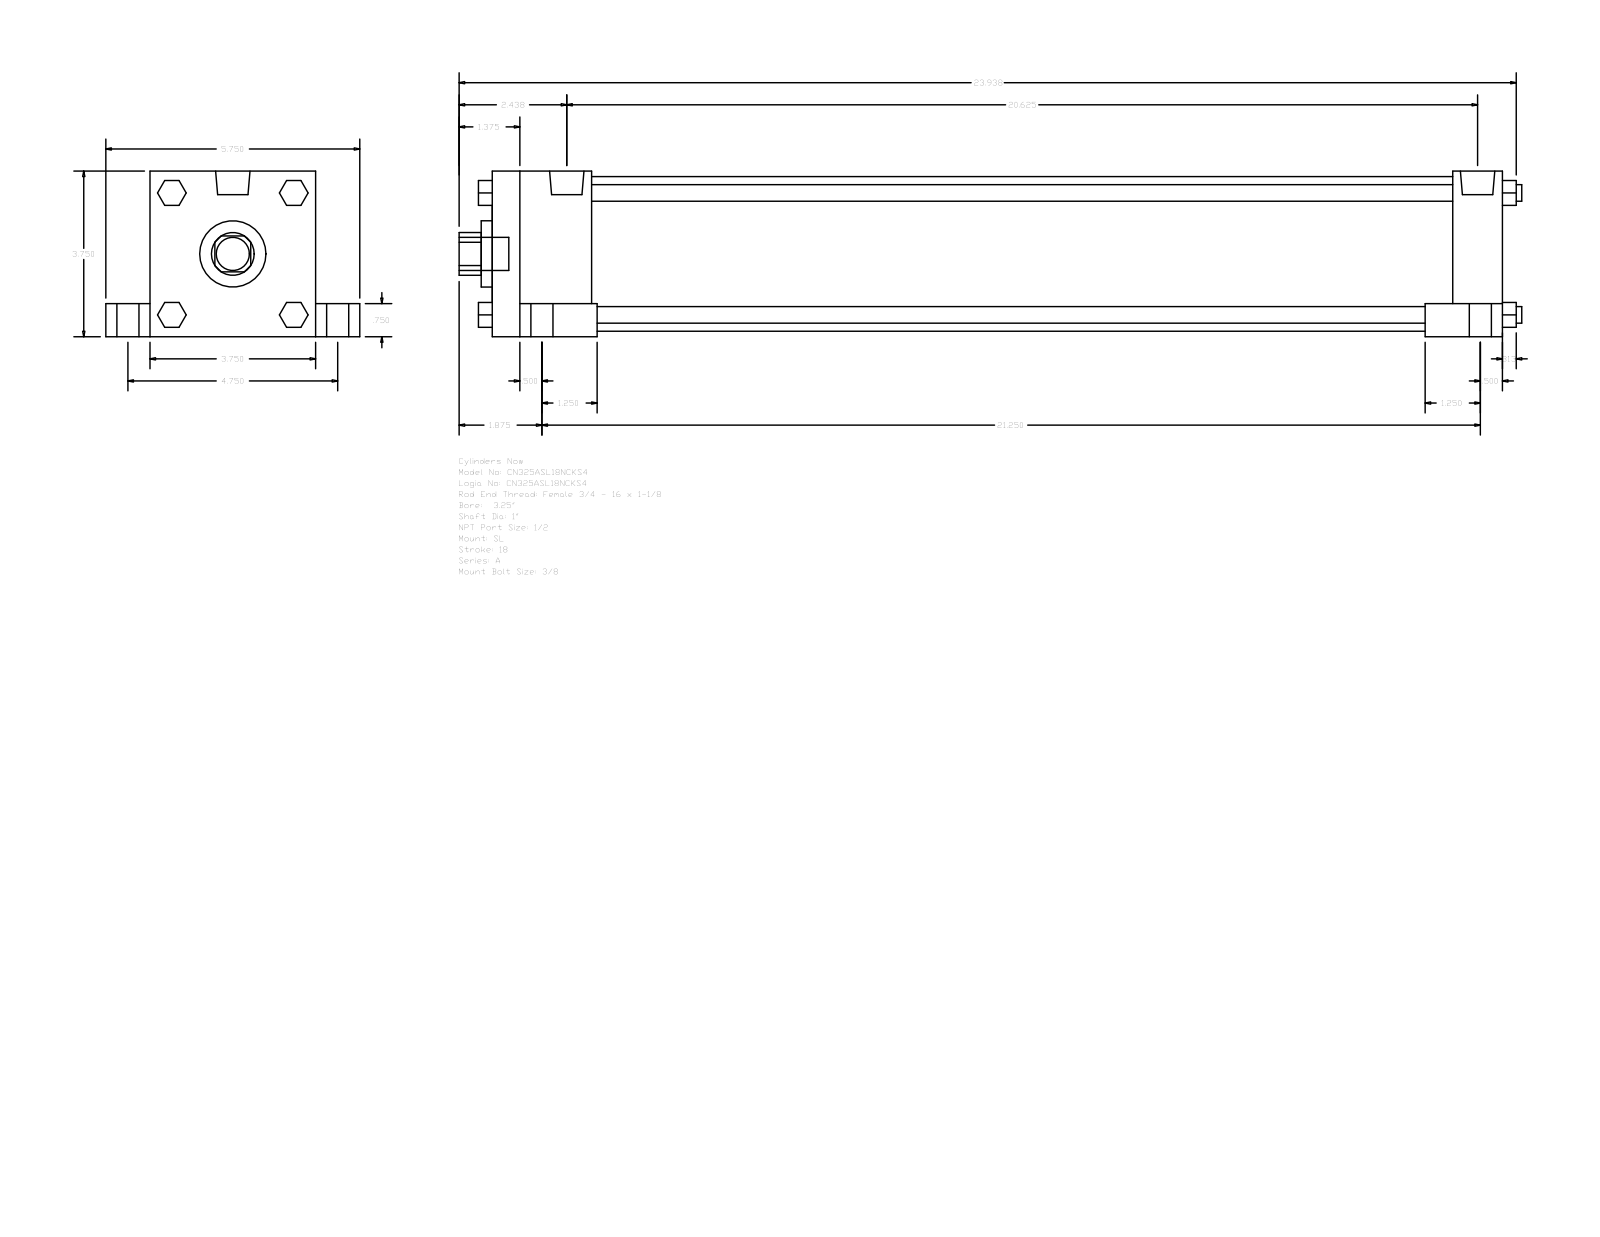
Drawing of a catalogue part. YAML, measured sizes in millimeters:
part_name: "A_SL__0325_1"
step_written_by: "GSSL Pune (CONFIG_CONTROL_DESIGN)"
units: millimeters
bodies: {solids: 0, faces: 150, planar: 114, cylindrical: 36, other: 0}
overall_size: [611.19, 146.05, 95.25]
round_holes:
  - {diameter: 25.4, count: 1}
  - {diameter: 38.1, count: 1}
  - {diameter: 88.9, count: 1}
round_bosses_or_shafts:
  - {diameter: 19.05, count: 5}
  - {diameter: 12.7, count: 4}
  - {diameter: 9.53, count: 4}
  - {diameter: 8.73, count: 4}
  - {diameter: 19.77, count: 2}
partial_cylinders:
  - {radius: 12.29, count: 1}
face_to_face_distances: [95.24, 581.03, 19.05, 25.41, 120.65, 76.19, 57.15, 552.45, 495.3, 523.88]
